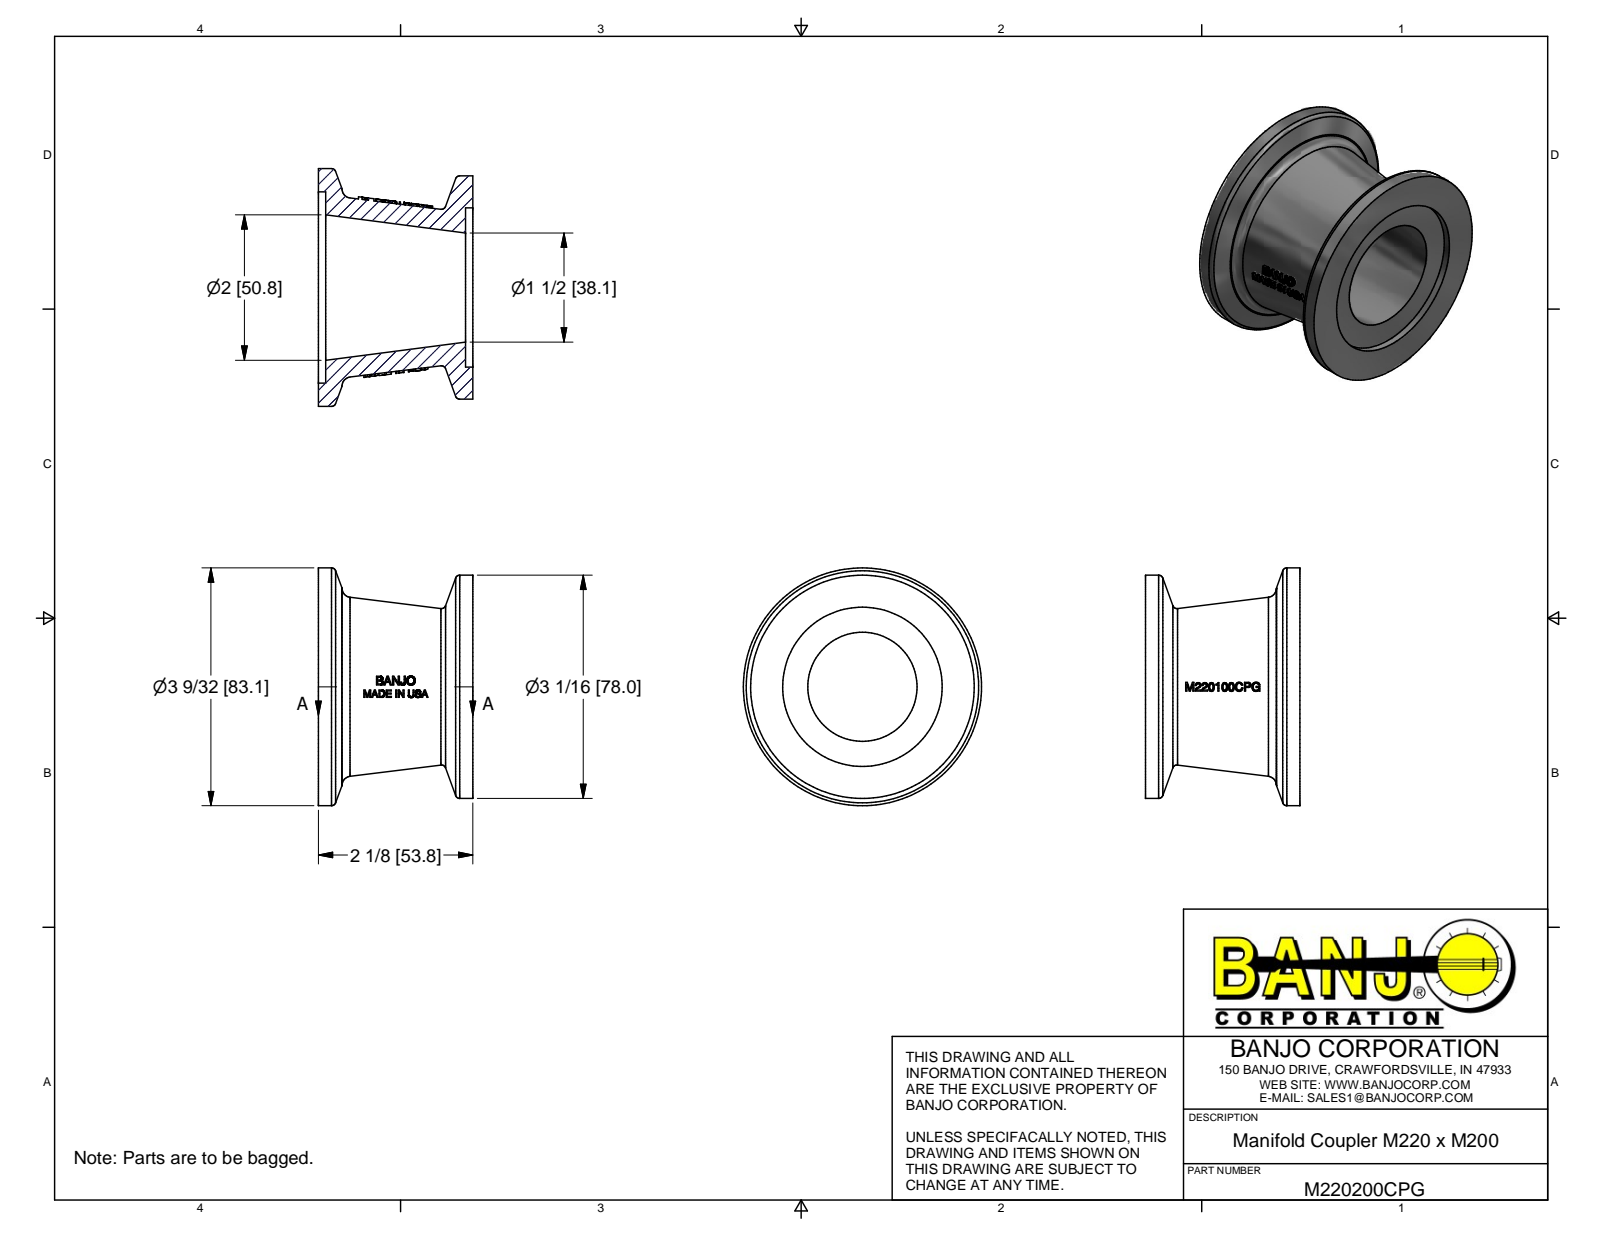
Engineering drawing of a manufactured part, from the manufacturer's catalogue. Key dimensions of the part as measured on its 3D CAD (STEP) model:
Part name (STEP PRODUCT): M220200CPG
STEP written by: Autodesk Inventor 2014 (AUTOMOTIVE_DESIGN)
Units: millimetres
Bodies: 1 solid, 350 faces (165 planar, 4 cylindrical, 181 other)
Overall size (bounding box): 83.06 × 83.06 × 53.85
Volume: 90 322 mm³ · Surface area: 29 234 mm²
Round holes (diameter × count): ⌀55.63 ×1, ⌀66.8 ×1
Round bosses / shafts (diameter × count): ⌀83.06 ×1, ⌀77.98 ×1
Main face-to-face distances: 2.54, 51.31, 53.85, 48.77, 2.87, 2.15, 3.05, 0.35, 14, 0.89
